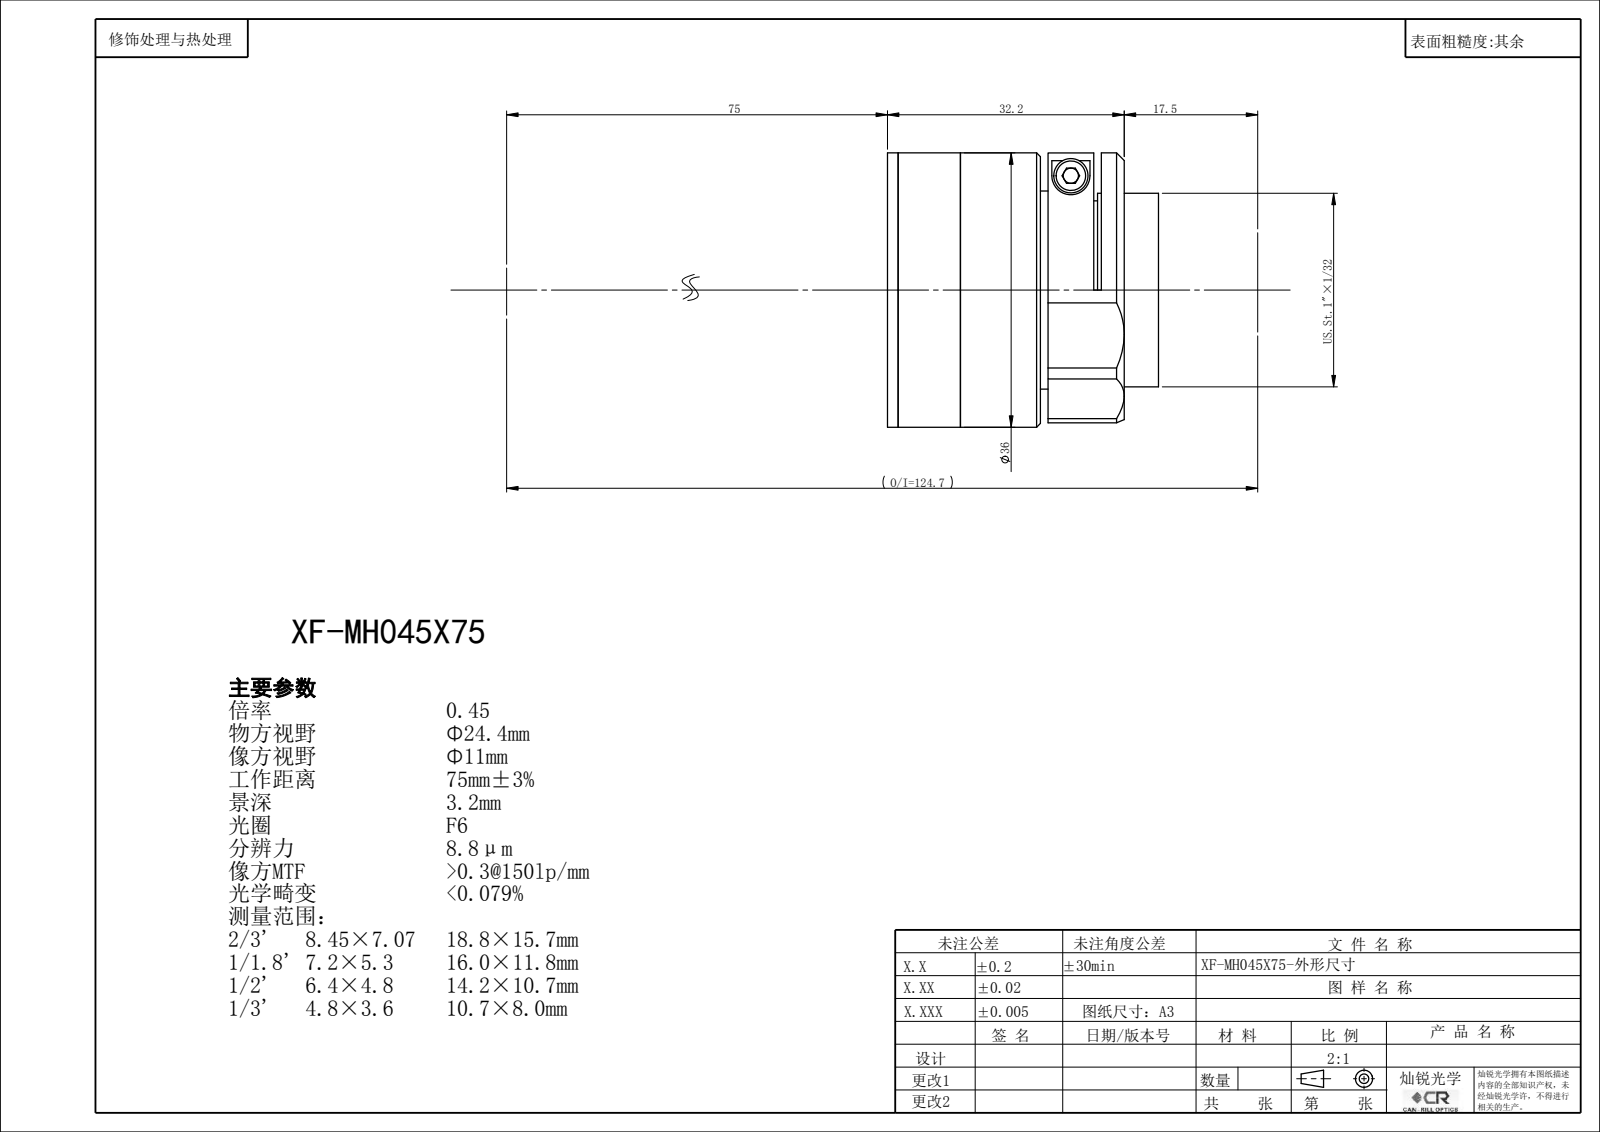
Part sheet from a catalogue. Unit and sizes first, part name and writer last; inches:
Units: inches
Overall size (bounding box): 1.426 × 1.417 × 1.417
Round holes (diameter × count): ⌀0.098 ×3, ⌀0.354 ×1, ⌀0.512 ×1, ⌀0.669 ×1, ⌀0.827 ×1, ⌀0.846 ×1, ⌀0.98 ×1, ⌀1.024 ×1
Round bosses / shafts (diameter × count): ⌀1.417 ×1, ⌀1.339 ×1, ⌀1.142 ×1, ⌀1 ×1, ⌀0.945 ×1
Main face-to-face distances: 1.213, 0.055, 1.268, 1.209, 0.059, 1.154, 0.039, 0.079, 0.217, 1.126
Bodies: 0 solids, 84 faces (38 planar, 38 cylindrical, 8 other)
Part name (STEP PRODUCT): XF-MH045X75
STEP written by: SolidWorks 2022 (CONFIG_CONTROL_DESIGN)
